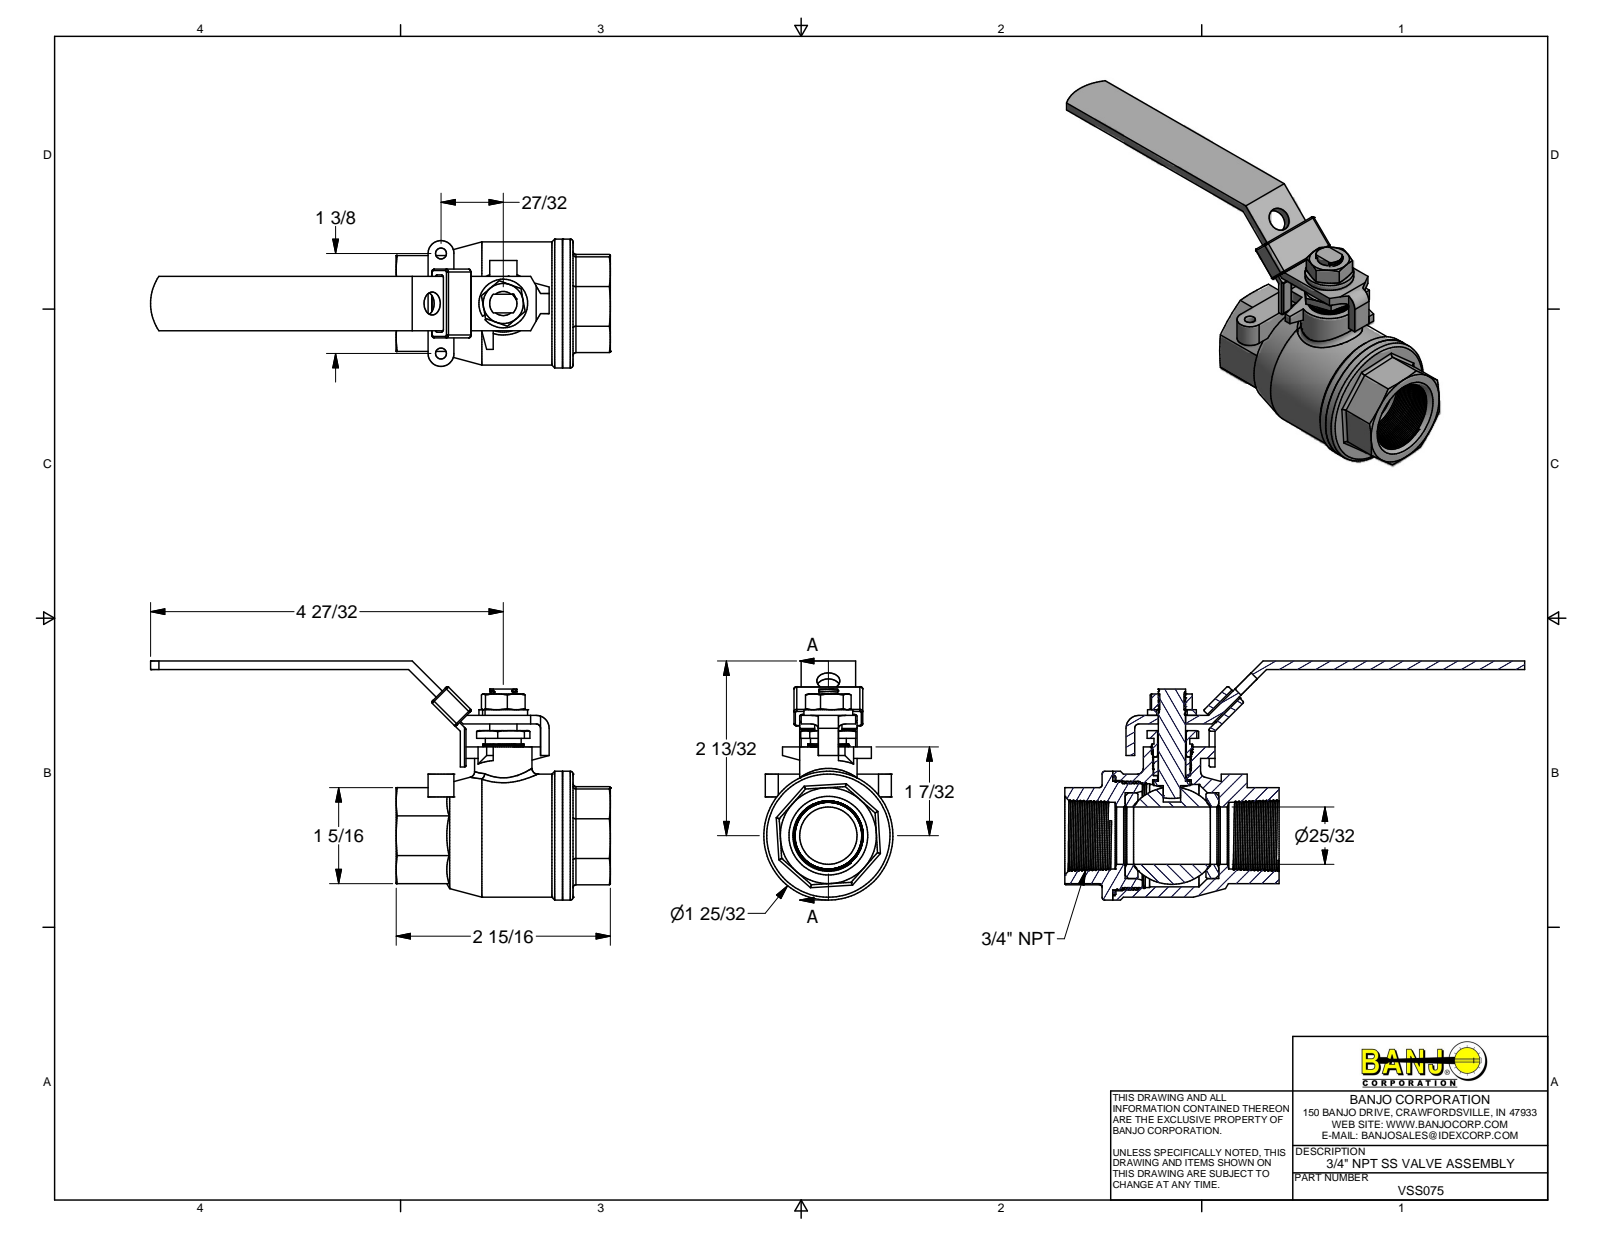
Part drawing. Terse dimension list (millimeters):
name: VSS075
written by: Autodesk Inventor 2013 (AUTOMOTIVE_DESIGN)
unit: mm
bodies: 14 solids, 380 faces (142 planar, 117 cylindrical, 121 other)
size: 160.35 × 83.5 × 45
volume: 75 670 mm³; area: 47 015 mm²
holes: 2× ⌀3.8, 1× ⌀8, 1× ⌀8.43, 1× ⌀10, 1× ⌀10.6, 1× ⌀13, 1× ⌀13.5, 1× ⌀20, 1× ⌀30, 1× ⌀35.8, 1× ⌀36.3, 1× ⌀38.5
bosses: 1× ⌀45, 1× ⌀43, 1× ⌀41, 1× ⌀38, 1× ⌀20, 1× ⌀17, 1× ⌀14.28, 1× ⌀12.8
rounds: 16× R1, 15× R0.5, 3× R4.5, 1× R1.5, 1× R17, 1× R20
face distances: 3, 8, 19, 33.5, 2, 6, 5.5, 0.5, 2.5, 3.5
hole spacings: 27.87, 34.94
